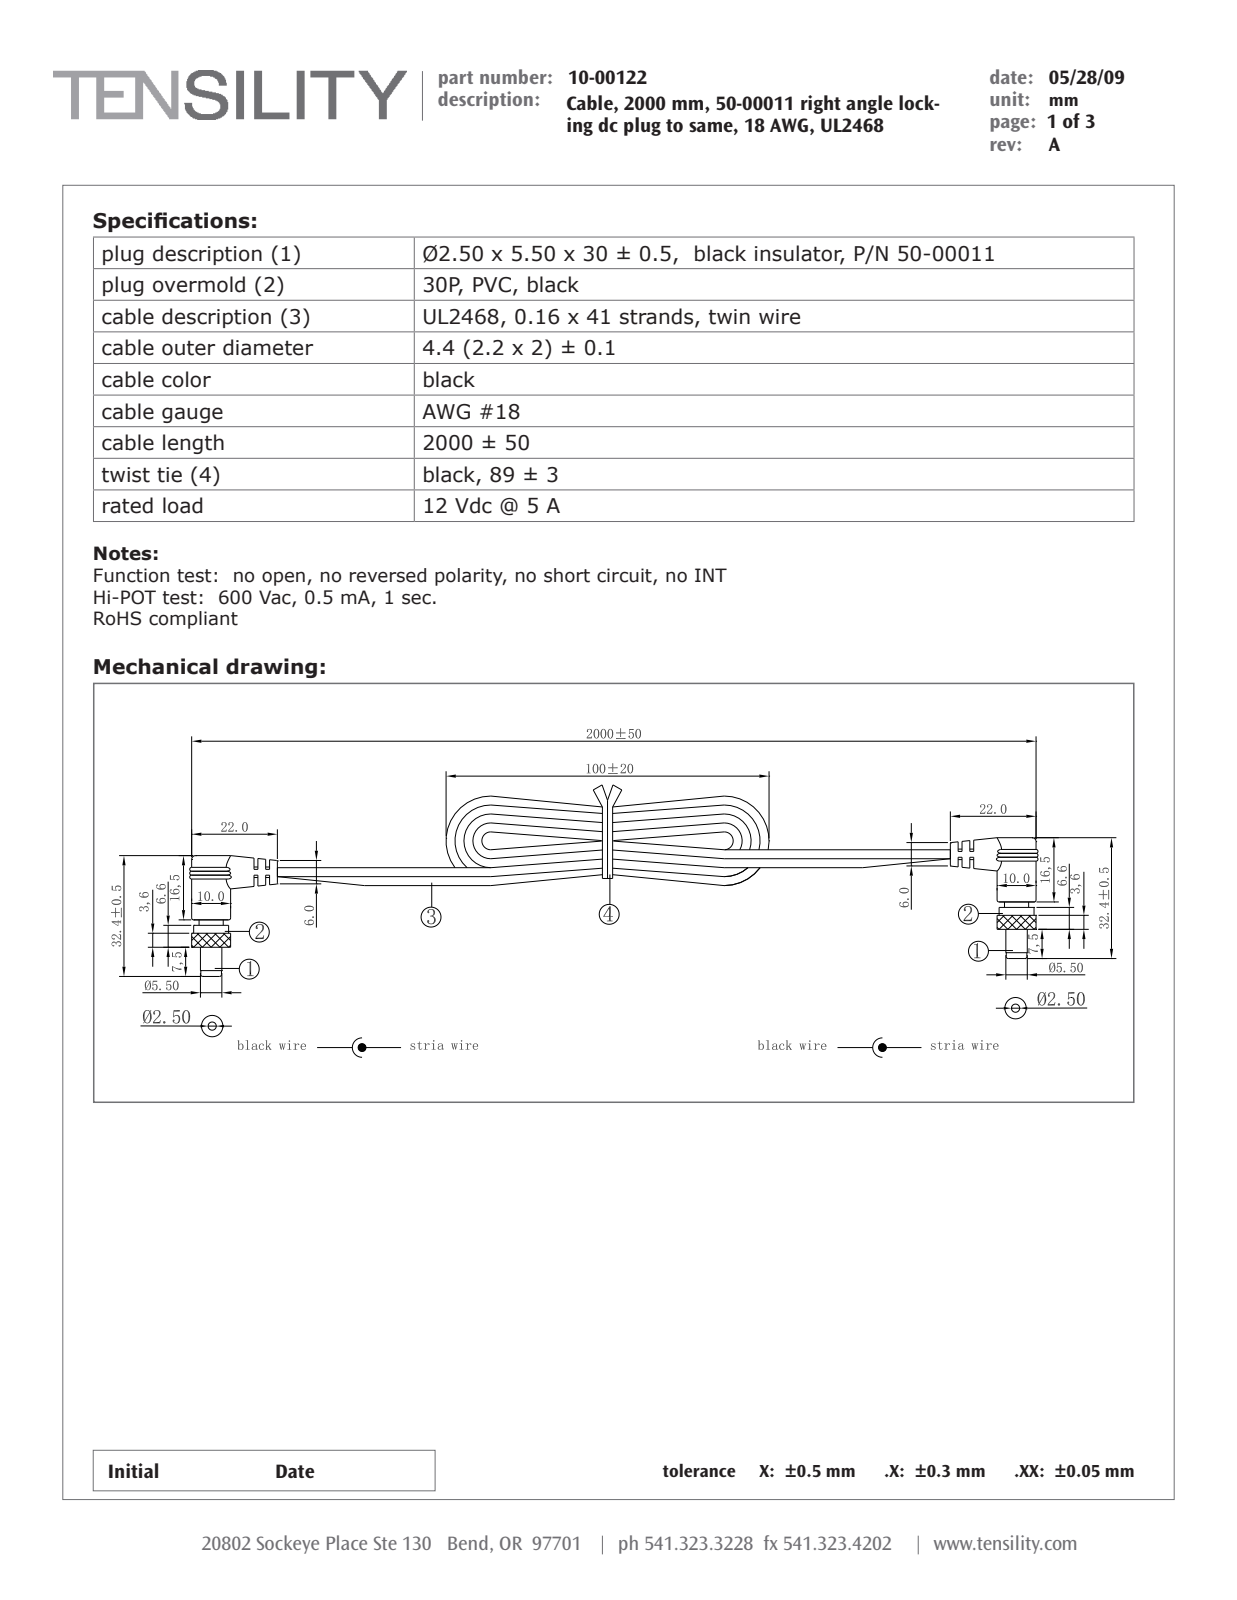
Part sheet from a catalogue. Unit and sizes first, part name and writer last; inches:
Units: inches
Overall size (bounding box): 7.205 × 1.276 × 0.433
Round holes (diameter × count): ⌀0.063 ×2, ⌀0.085 ×2, ⌀0.098 ×2, ⌀0.118 ×2, ⌀0.128 ×2, ⌀0.167 ×2, ⌀0.198 ×2, ⌀0.214 ×2, ⌀0.217 ×2, ⌀0.222 ×2, ⌀0.252 ×2, ⌀0.285 ×2
Round bosses / shafts (diameter × count): ⌀0.433 ×2, ⌀0.394 ×2, ⌀0.276 ×2, ⌀0.244 ×2, ⌀0.236 ×2, ⌀0.216 ×2, ⌀0.209 ×2, ⌀0.087 ×2
Partial cylindrical surfaces — rounded edges, fillets, slot ends (radius × count): R0.022 ×8
Main face-to-face distances: 0.118, 0.039, 0.079, 0.65, 5.669, 5.748, 5.63, 0.72, 0.07, 5.787
Hole centre spacings: 6.772
Volume: 0.374 in³ · Surface area: 16.61 in²
Bodies: 22 solids, 2636 faces (733 planar, 459 cylindrical, 1444 other)
Part name (STEP PRODUCT): 50-00011; 30-00007_wbc; 50-00011 insulator; 50-00011 pin (+6 more)
STEP written by: SolidWorks 2015 (CONFIG_CONTROL_DESIGN)
